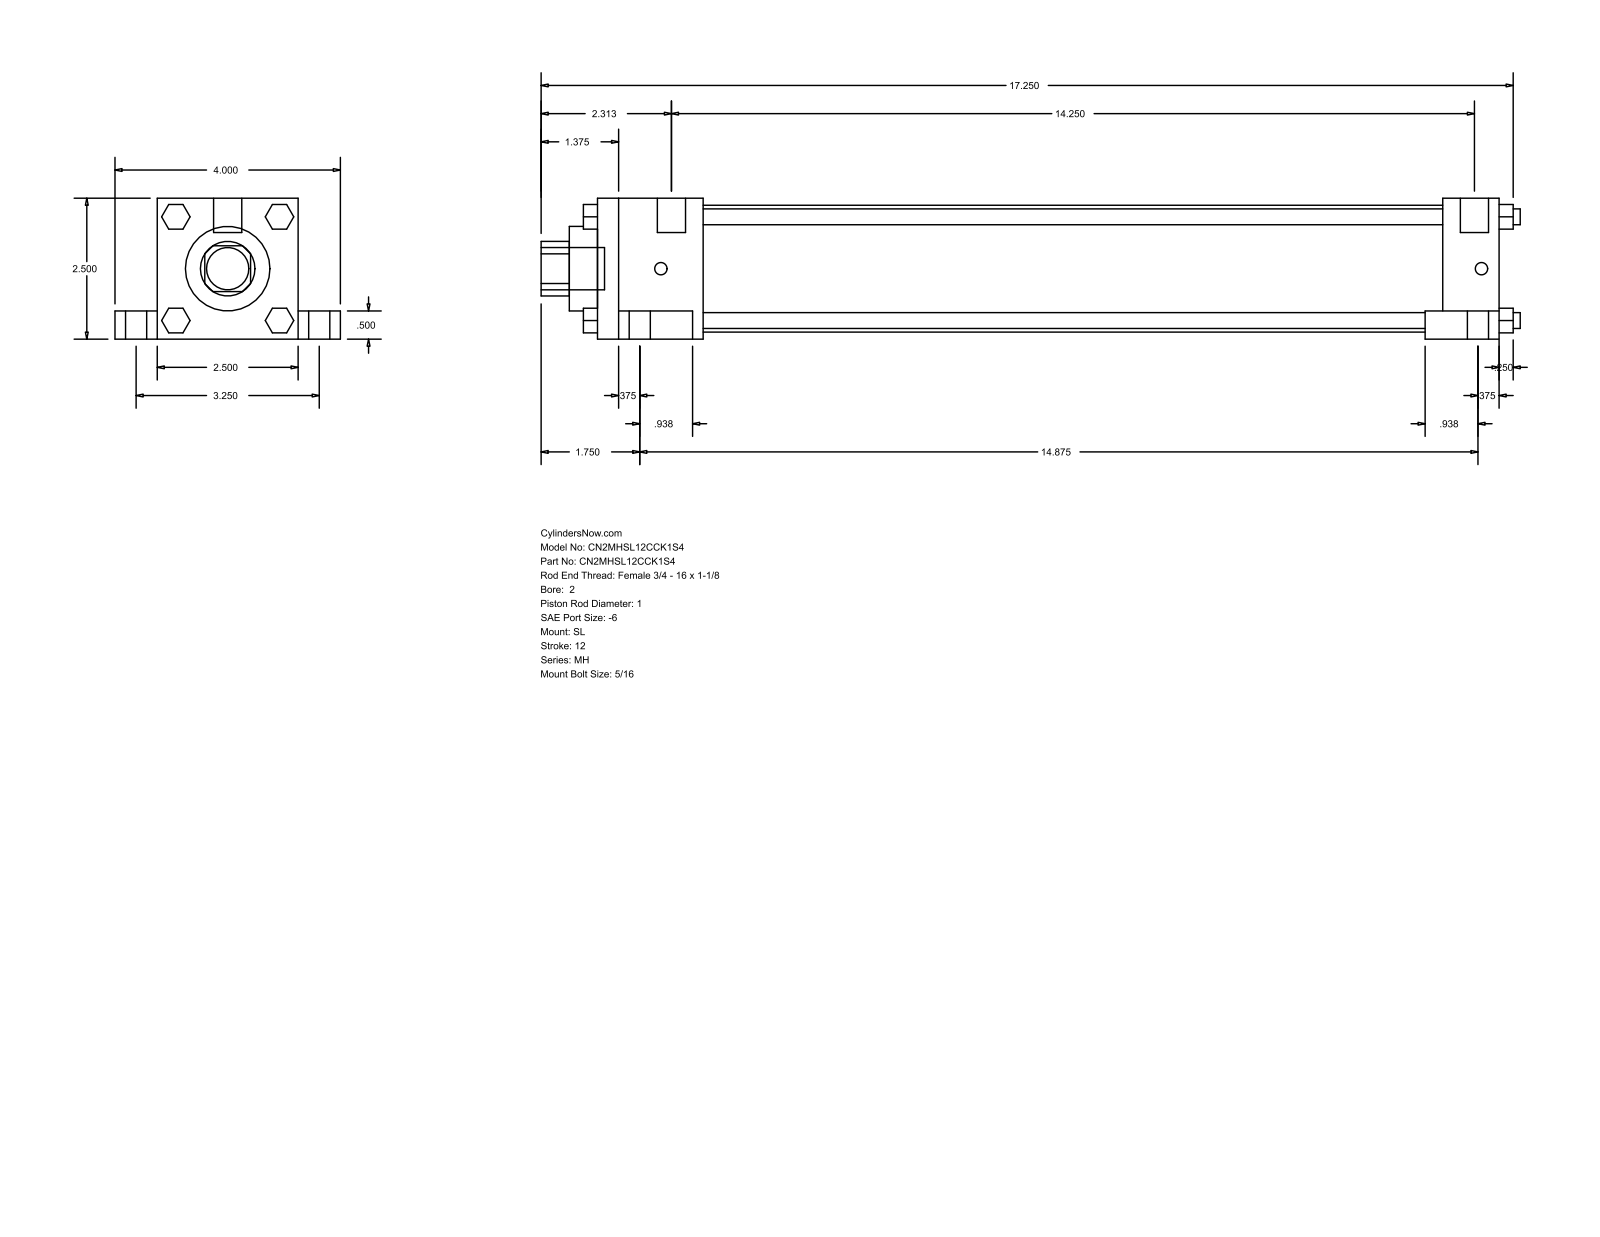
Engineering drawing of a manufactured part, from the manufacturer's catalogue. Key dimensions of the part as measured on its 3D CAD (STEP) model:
Part name (STEP PRODUCT): MH_SL__0200_1
STEP written by: GSSL Pune (CONFIG_CONTROL_DESIGN)
Units: millimetres
Bodies: 0 solids, 148 faces (112 planar, 36 cylindrical, 0 other)
Overall size (bounding box): 441.32 × 101.6 × 63.5
Round holes (diameter × count): ⌀25.4 ×1, ⌀38.1 ×1, ⌀57.15 ×1
Round bosses / shafts (diameter × count): ⌀15.88 ×4, ⌀9.53 ×4, ⌀7.14 ×4, ⌀5.56 ×4, ⌀12.7 ×2, ⌀19.05 ×1
Partial cylindrical surfaces — rounded edges, fillets, slot ends (radius × count): R12.29 ×1
Main face-to-face distances: 63.5, 406.4, 12.7, 19.05, 50.8, 82.55, 9.52, 25.4, 381, 47.63
